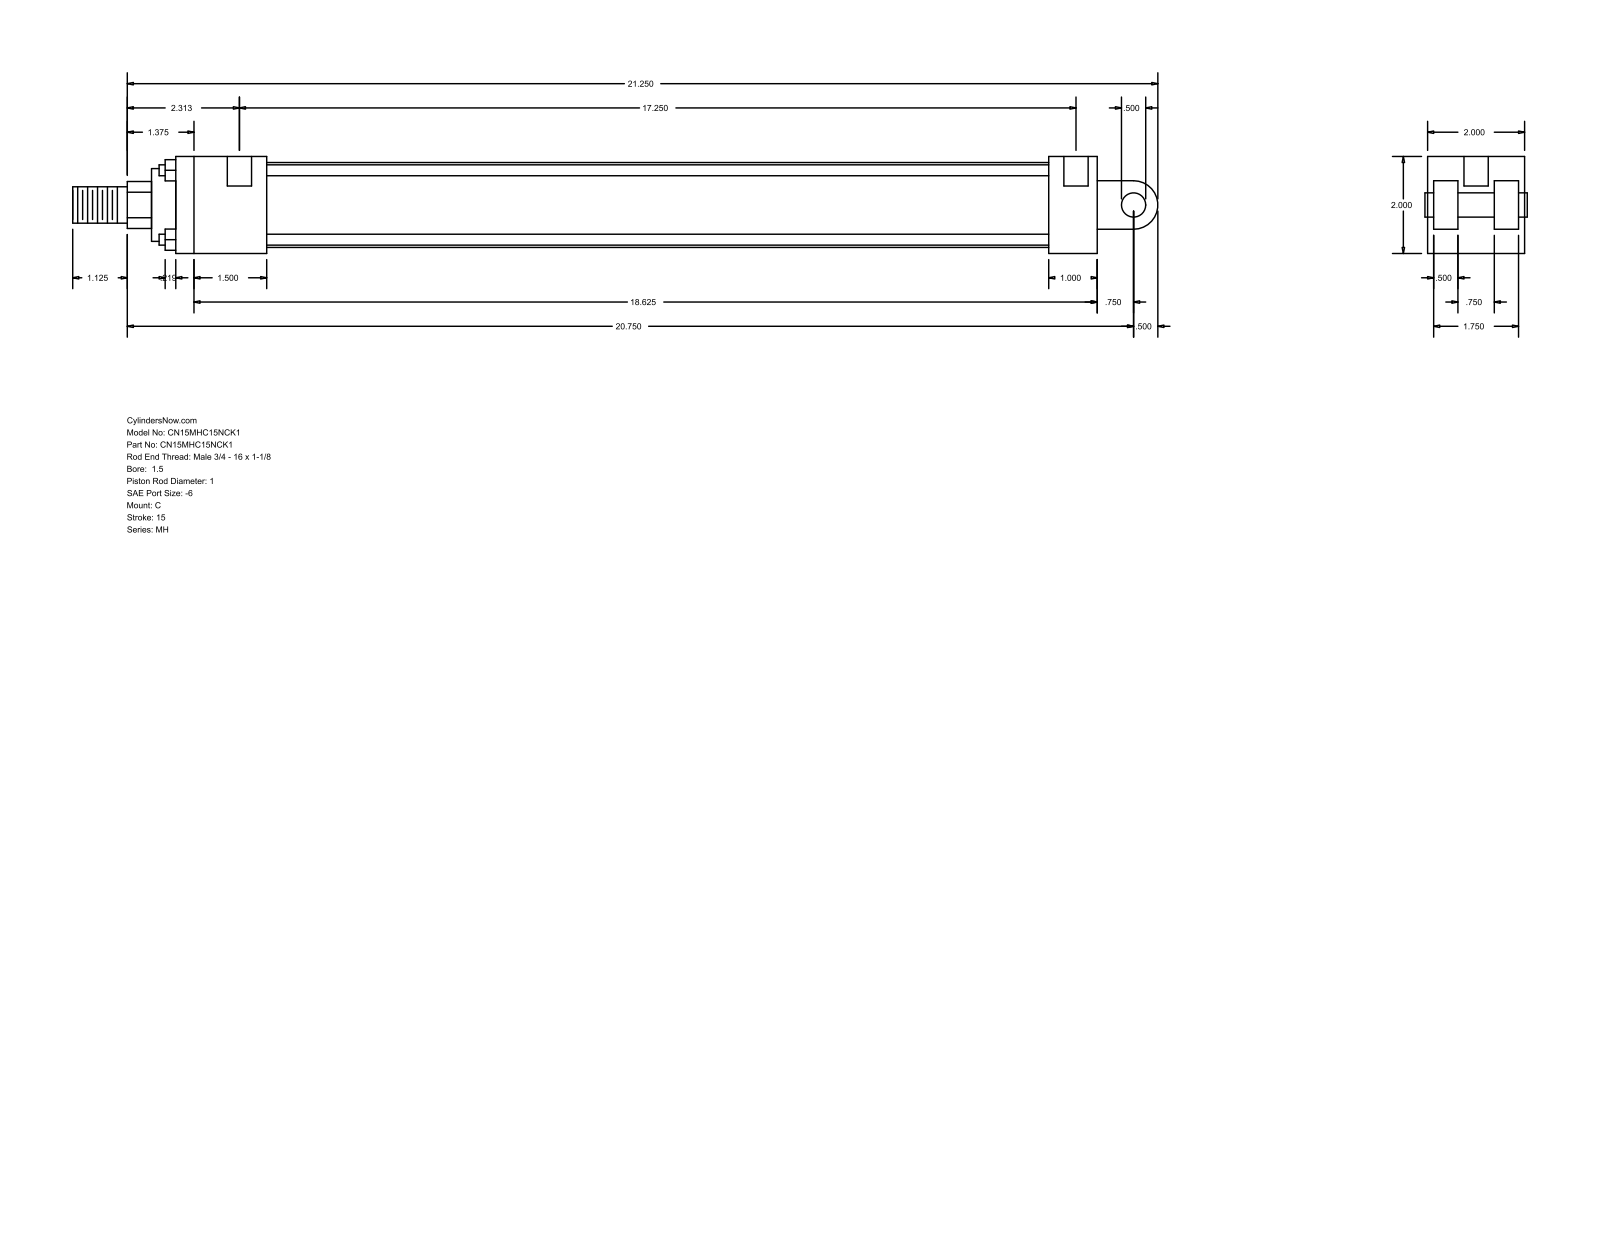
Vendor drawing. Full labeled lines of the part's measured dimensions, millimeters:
Part name (STEP PRODUCT): MH_C__0150_1
STEP written by: GSSL Pune (CONFIG_CONTROL_DESIGN)
Units: millimetres
Bodies: 0 solids, 99 faces (70 planar, 29 cylindrical, 0 other)
Overall size (bounding box): 568.33 × 50.8 × 50.8
Round holes (diameter × count): ⌀5.56 ×4, ⌀12.7 ×2
Round bosses / shafts (diameter × count): ⌀5.71 ×4, ⌀44.45 ×1, ⌀38.1 ×1, ⌀25.4 ×1, ⌀19.05 ×1, ⌀12.7 ×1
Partial cylindrical surfaces — rounded edges, fillets, slot ends (radius × count): R12.29 ×1, R12.7 ×1
Main face-to-face distances: 50.8, 12.7, 47.63, 25.4, 3.17, 15.87, 34.93, 31.76, 482.6, 38.1
Hole centre spacings: 441.33, 3.18, 438.15
